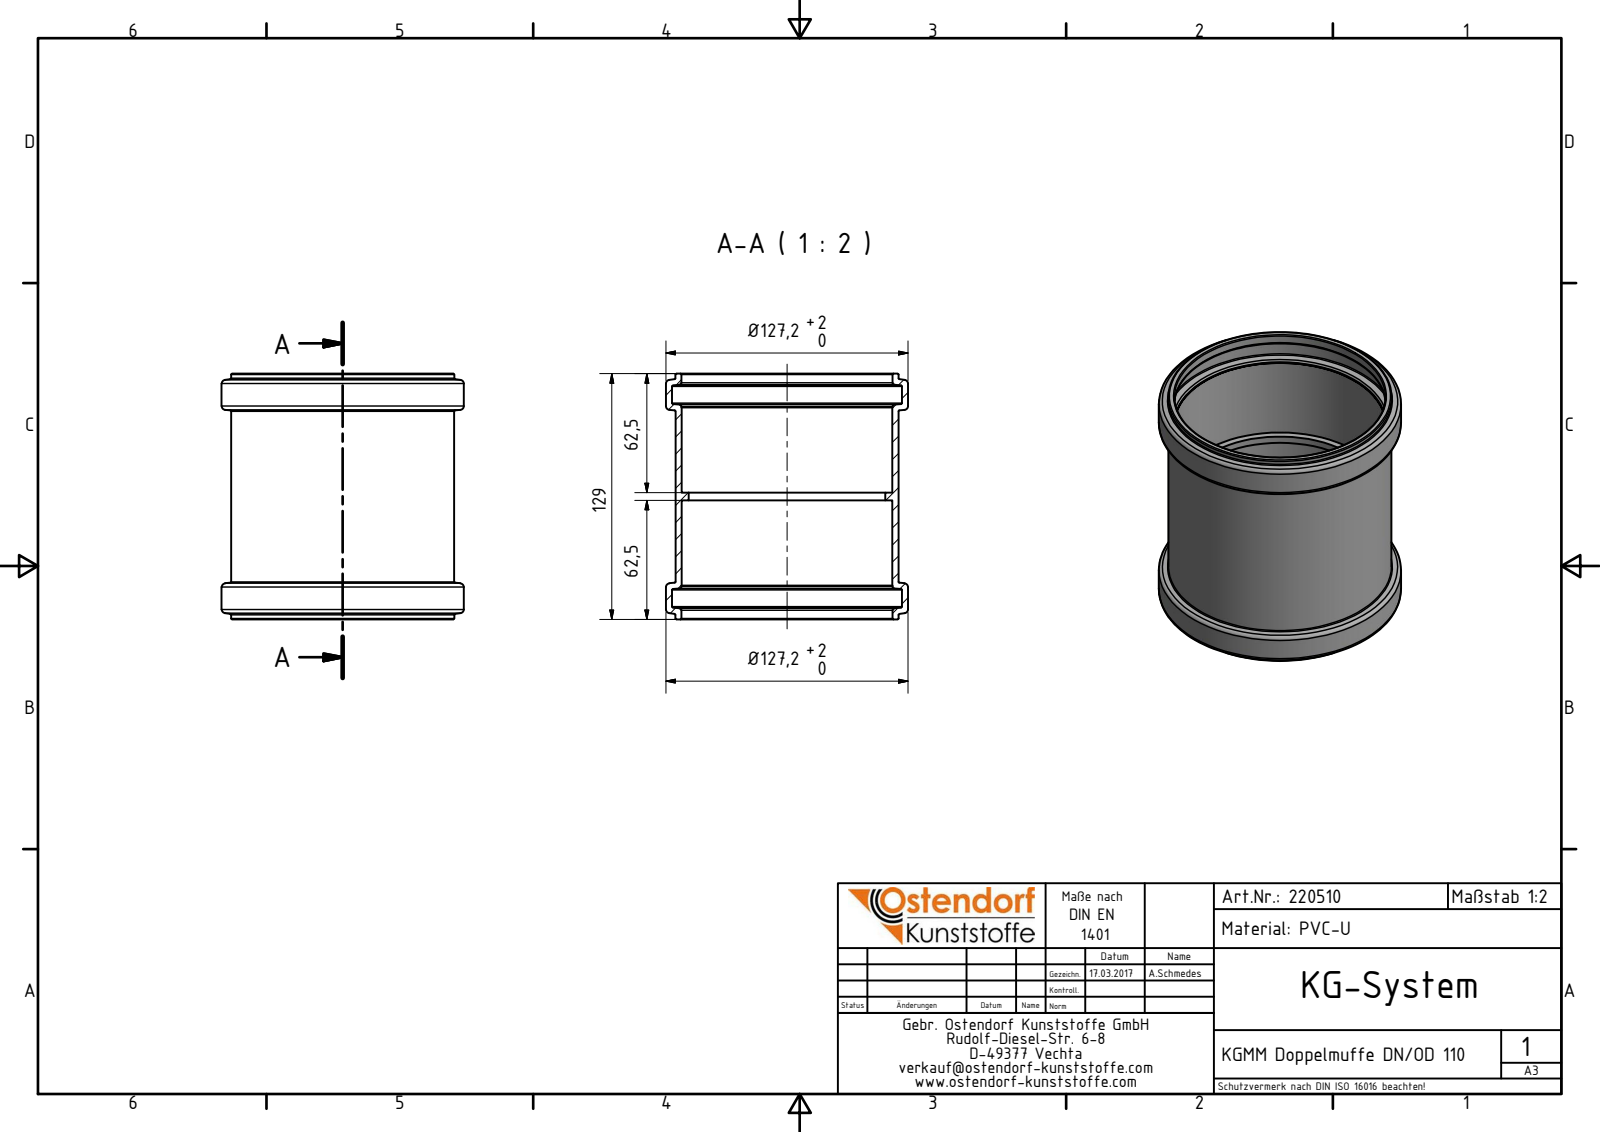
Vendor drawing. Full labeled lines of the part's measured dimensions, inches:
Part name (STEP PRODUCT): 220510 KGMM Doppelmuffe DN_OD 110
STEP written by: Autodesk Inventor 2016 (AUTOMOTIVE_DESIGN)
Units: inches
Bodies: 1 solid, 48 faces (6 planar, 14 cylindrical, 28 other)
Overall size (bounding box): 5.079 × 5.008 × 5.008
Volume: 10.72 in³ · Surface area: 170.3 in²
Round holes (diameter × count): ⌀4.067 ×1, ⌀4.358 ×1, ⌀4.362 ×1, ⌀4.756 ×1
Round bosses / shafts (diameter × count): ⌀5.008 ×1, ⌀4.614 ×1, ⌀4.61 ×1
Main face-to-face distances: 2.461, 2.618, 0.157, 5.079, 0.699, 4.38, 1.761, 1.919, 3.68
